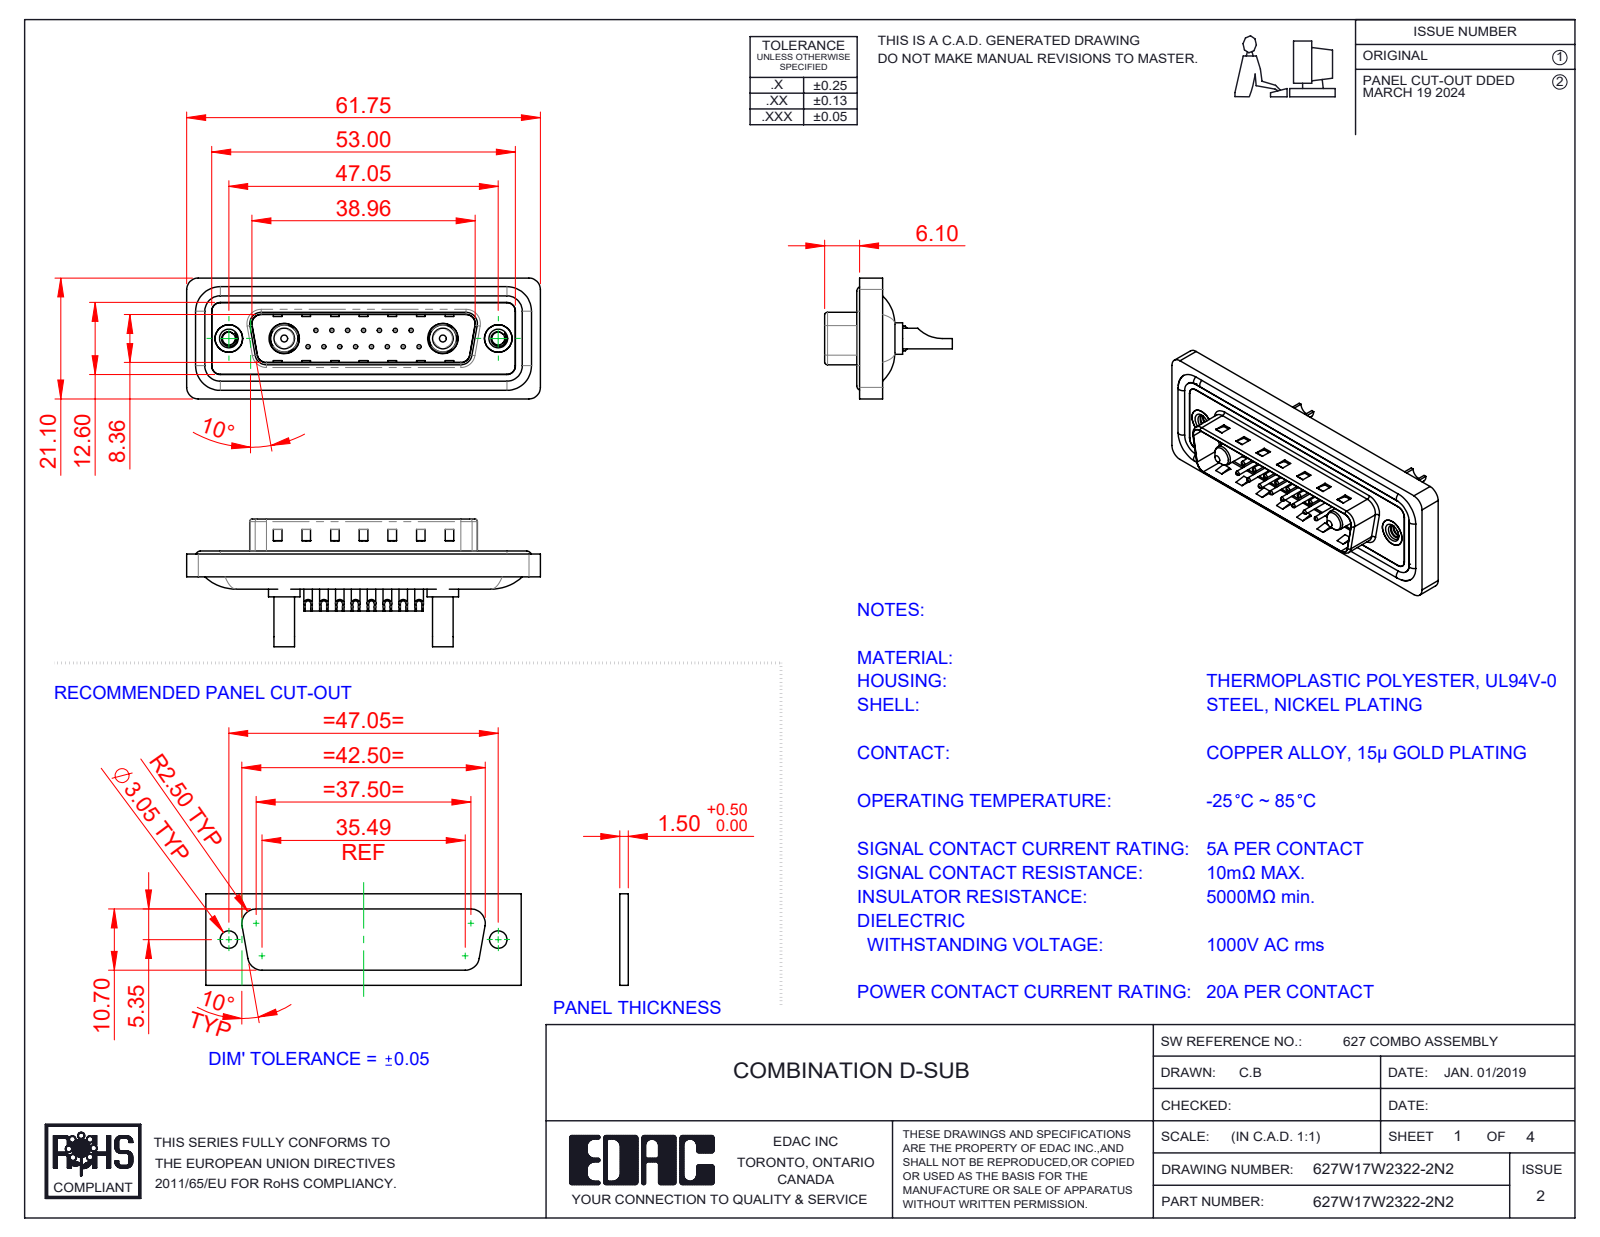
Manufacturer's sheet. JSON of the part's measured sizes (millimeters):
{"part_name": "627W17W2322-2N2; 627Combo Contact Row 2_22; 627Combo Threaded Rivet_2; Power Pin_20A SC (+5 more)", "step_written_by": "SolidWorks 2023 (CONFIG_CONTROL_DESIGN)", "units": "millimeters", "bodies": {"solids": 26, "faces": 1130, "planar": 370, "cylindrical": 472, "other": 288}, "overall_size": [61.75, 22.3, 21.1], "volume_mm3": 7315, "surface_area_mm2": 12198, "round_holes": [[0.75, 15], [1, 15], [1.6, 15], [2, 15], [2.26, 2], [2.7, 2], [4, 2], [4.8, 2], [4.85, 2], [5, 2], [5.3, 2]], "round_bosses_or_shafts": [[1.5, 15], [1.6, 4], [5.5, 2], [5.2, 2], [4.9, 2], [4.75, 2], [3.75, 2], [3.6, 2]], "partial_cylinders_radius": [[1.5, 22], [2, 18], [0.5, 8], [1.6, 8], [1, 6], [0.25, 4], [0.6, 4], [0.65, 4]], "face_to_face_distances": [0.4, 1.5, 1.1, 1.6, 0.5, 3.1, 2.9, 0.82, 9.58, 4.1], "hole_center_spacings": [3.16, 2.77, 5.54, 8.31, 5.04, 7.49, 11.08, 5.03]}
